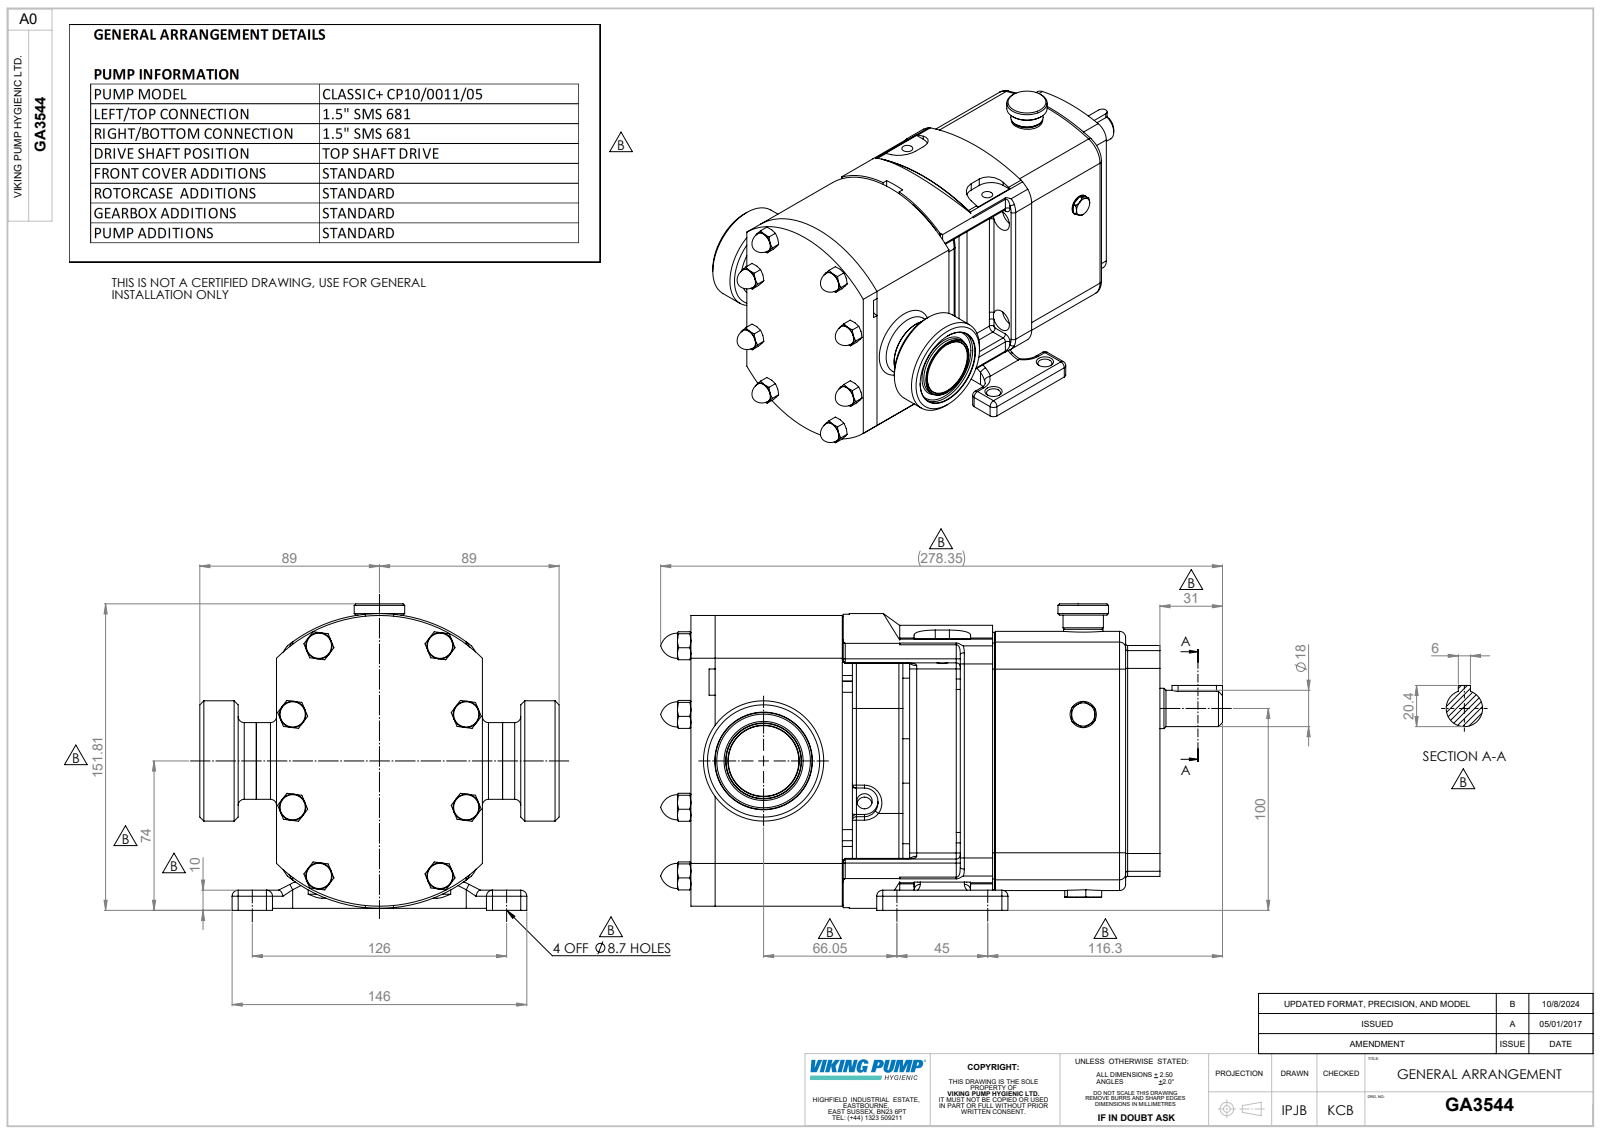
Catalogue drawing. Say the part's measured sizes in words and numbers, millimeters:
The part is named "Copy of Z94-5101-22 - 1.5 INCH SMS681^GA3544; Copy (2) of CP10-0011-05 H T^GA3544; GA3544". Its 3-D file was written by "SolidWorks 2023 (AUTOMOTIVE_DESIGN)". It is 3 solids with 782 faces: 256 planar, 226 cylindrical and 300 other. Overall it measures 278.35 by 178 by 151.81 millimeters. Its volume is 2 664 000 cubic millimeters and its surface area 202 953 square millimeters. Round holes: 4 of diameter 8.7, 4 of diameter 14, 2 of diameter 6.8, 2 of diameter 7.63, 1 of diameter 22.53, 1 of diameter 35, 1 of diameter 48. Round bosses or shafts: 2 of diameter 30, 1 of diameter 59.6, 1 of diameter 38, 1 of diameter 37.6, 1 of diameter 25.02, 1 of diameter 19.99, 1 of diameter 19.98, 1 of diameter 19.5. Partial cylindrical surfaces (rounded edges, fillets, slot ends): 30 of radius 2, 26 of radius 3, 12 of radius 13.5, 8 of radius 10.5, 6 of radius 3.5, 4 of radius 5.5, 4 of radius 6, 4 of radius 9. The main face-to-face distances are 5, 102, 232.35, 124, 19, 96.99, 5.01, 21, 91.99, 97. The hole center spacings are 35.92, 100.55, 45, 76, 77.02, 108.2, 126, 133.79.
